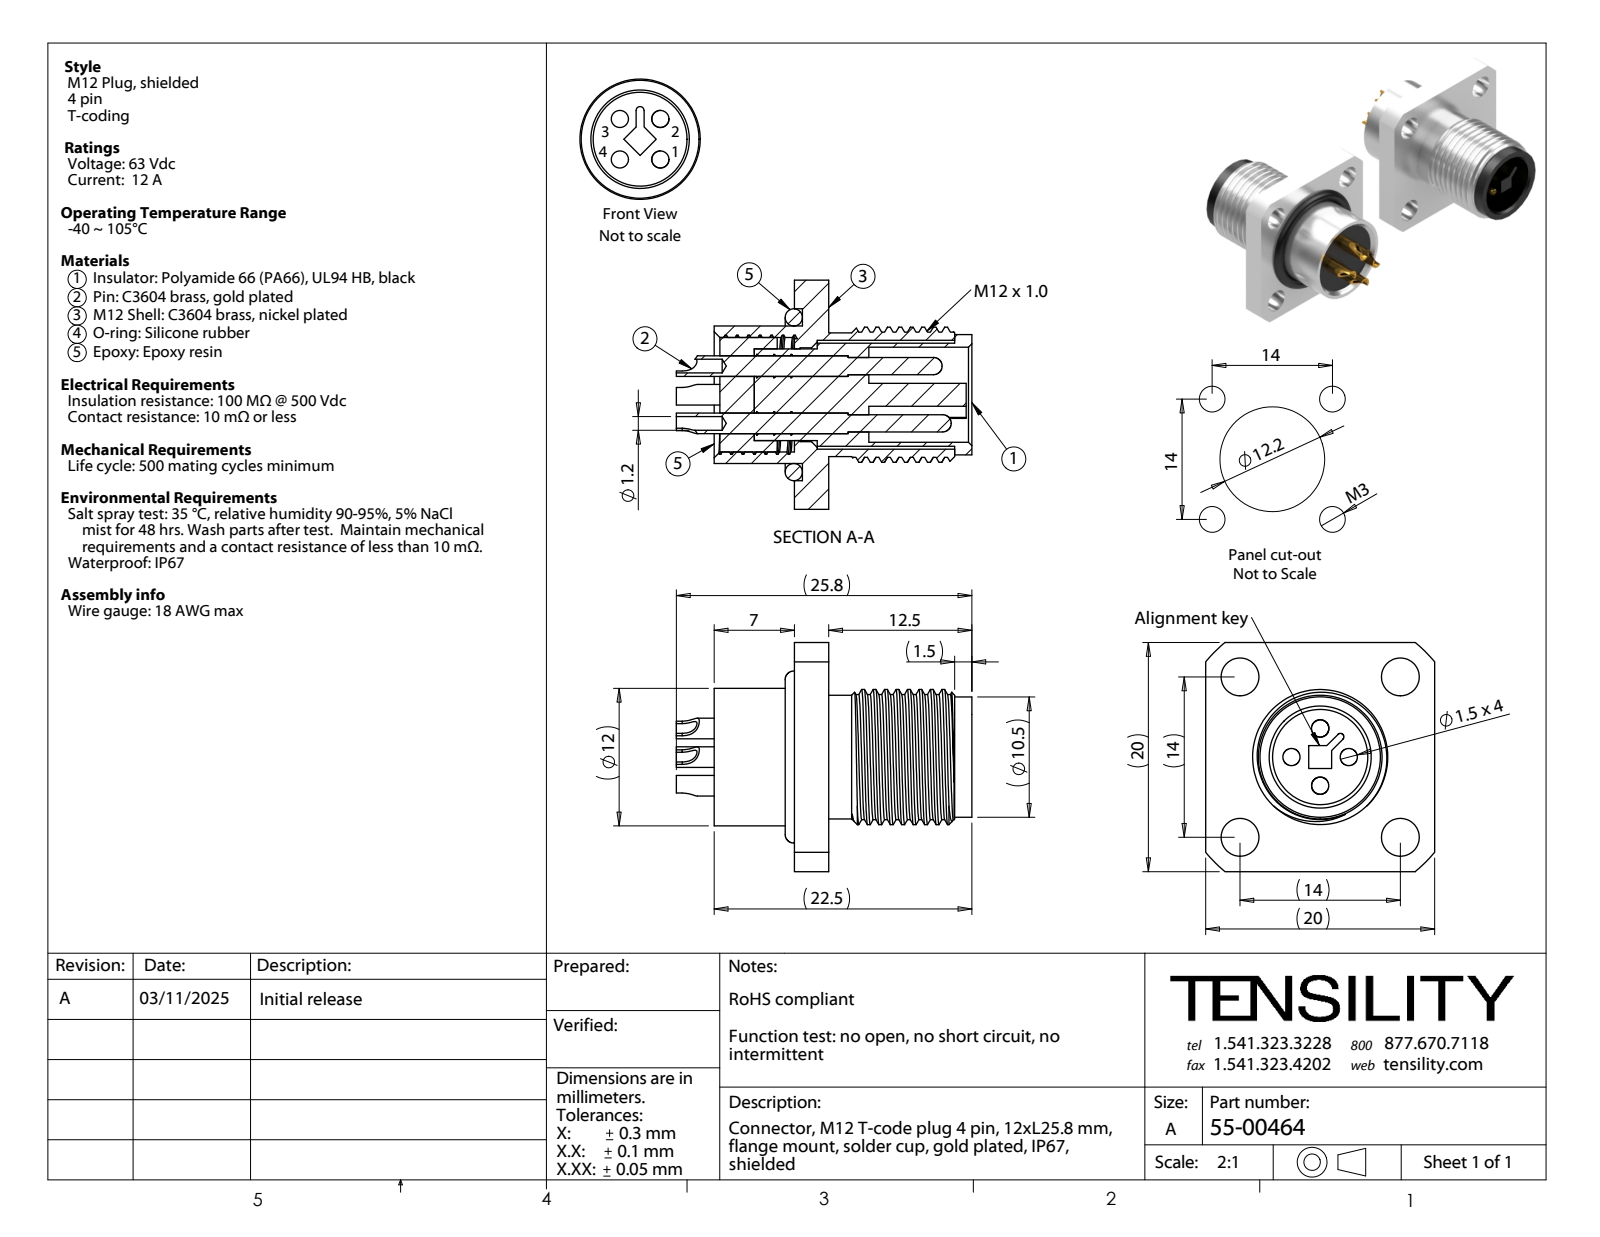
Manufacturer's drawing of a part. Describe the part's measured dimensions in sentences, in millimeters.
The part is named "55-00464-01; 55-00464-02; 55-00464-03; 55-00464-04 (+2 more)". Its 3-D file was written by "SolidWorks 2021 (CONFIG_CONTROL_DESIGN)". It is 8 solids with 298 faces: 60 planar, 167 cylindrical and 71 other. Overall it measures 25.8 by 20 by 20 millimeters. Its volume is 2 549 cubic millimeters and its surface area 4 913 square millimeters. Round holes: 4 of diameter 1.2, 4 of diameter 1.5, 4 of diameter 3.3, 1 of diameter 8, 1 of diameter 8.2, 1 of diameter 8.3, 1 of diameter 9.5, 1 of diameter 10, 1 of diameter 15. Round bosses or shafts: 4 of diameter 1.8, 1 of diameter 12, 1 of diameter 11.8, 1 of diameter 10.92, 1 of diameter 10.8, 1 of diameter 10.5, 1 of diameter 9. Partial cylindrical surfaces (rounded edges, fillets, slot ends): 2 of radius 1.7, 1 of radius 0.3, 1 of radius 13. The main face-to-face distances are 3, 6.5, 3.5, 11, 9, 20, 2, 2.3, 9.5, 4.2. The hole center spacings are 8.32, 11.8, 2.5, 3.54, 9.9, 14, 5, 19.8.
